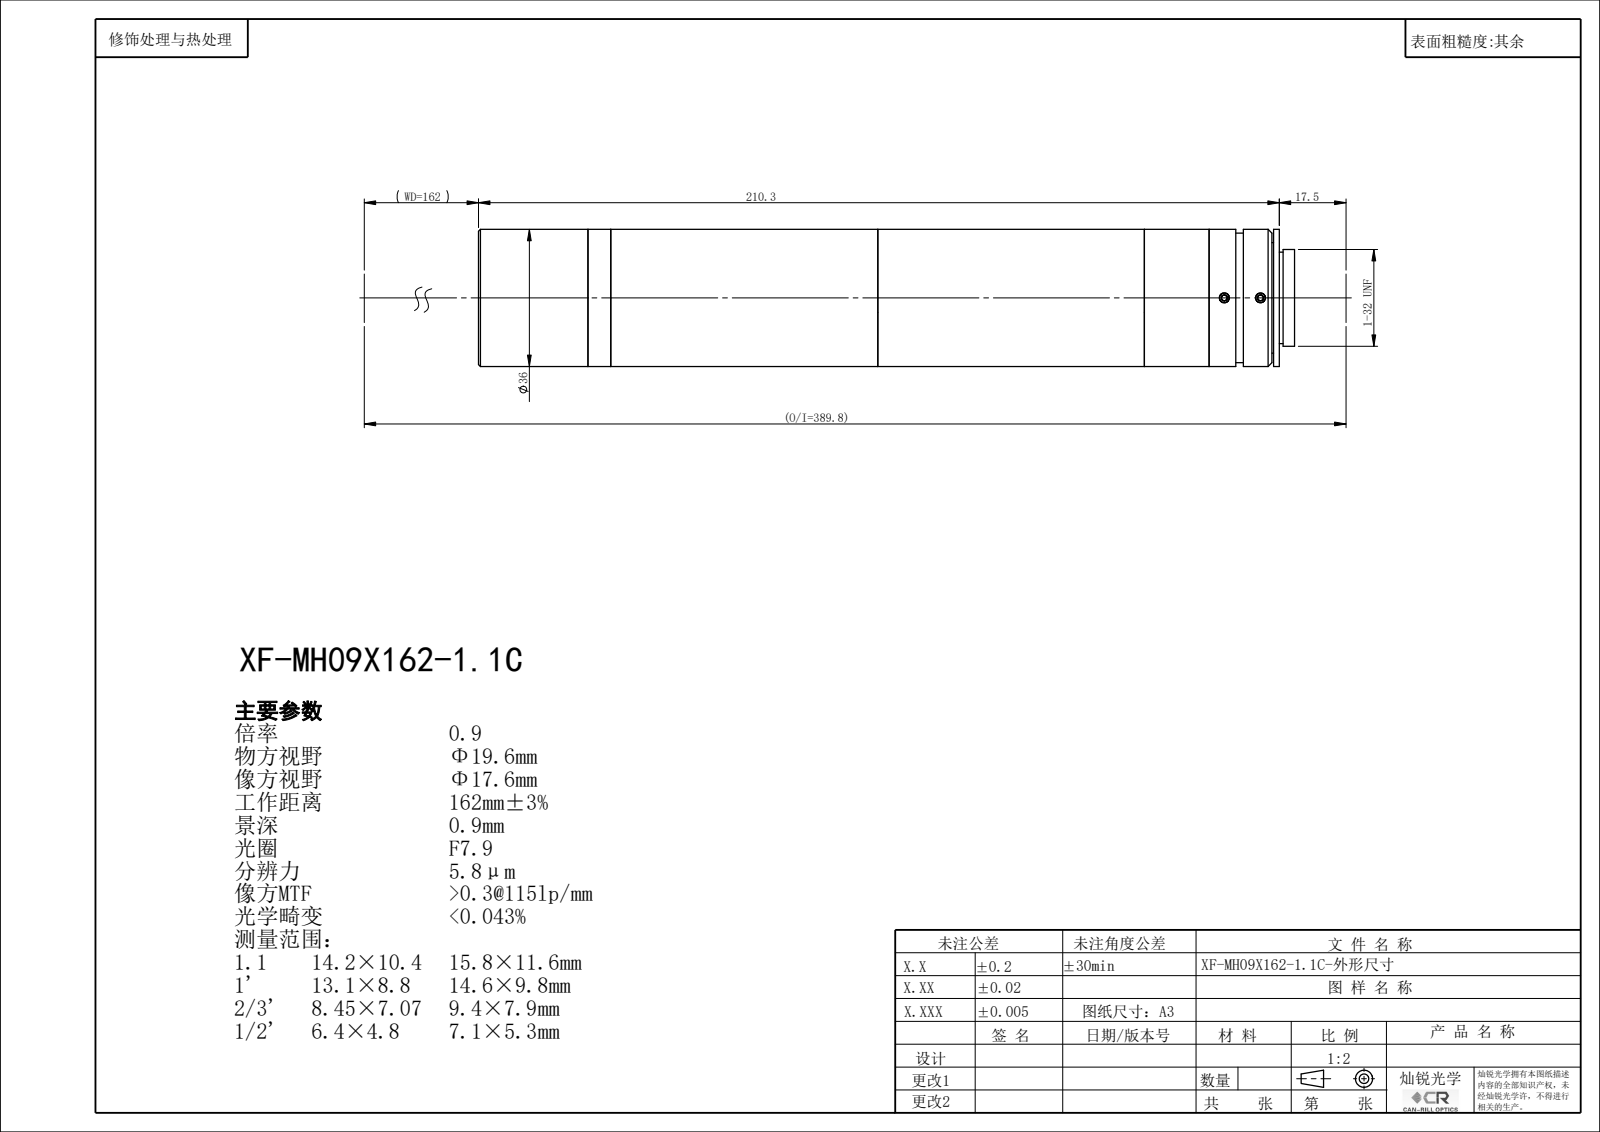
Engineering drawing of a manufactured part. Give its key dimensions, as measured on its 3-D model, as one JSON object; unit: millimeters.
{"part_name": "XF-MH09X162-1.1C", "step_written_by": "SolidWorks 2022 (CONFIG_CONTROL_DESIGN)", "units": "millimeters", "bodies": {"solids": 0, "faces": 128, "planar": 66, "cylindrical": 40, "other": 22}, "overall_size": [214.28, 36, 36], "round_holes": [[2.5, 3], [22.4, 1], [24, 1], [26, 1], [29.4, 1], [33.4, 1], [34.5, 1]], "round_bosses_or_shafts": [[36, 1], [34, 1], [25.4, 1]], "face_to_face_distances": [18.43, 1.5, 16.93, 87, 103.93, 105.43, 6, 93, 10.93, 12.43]}
